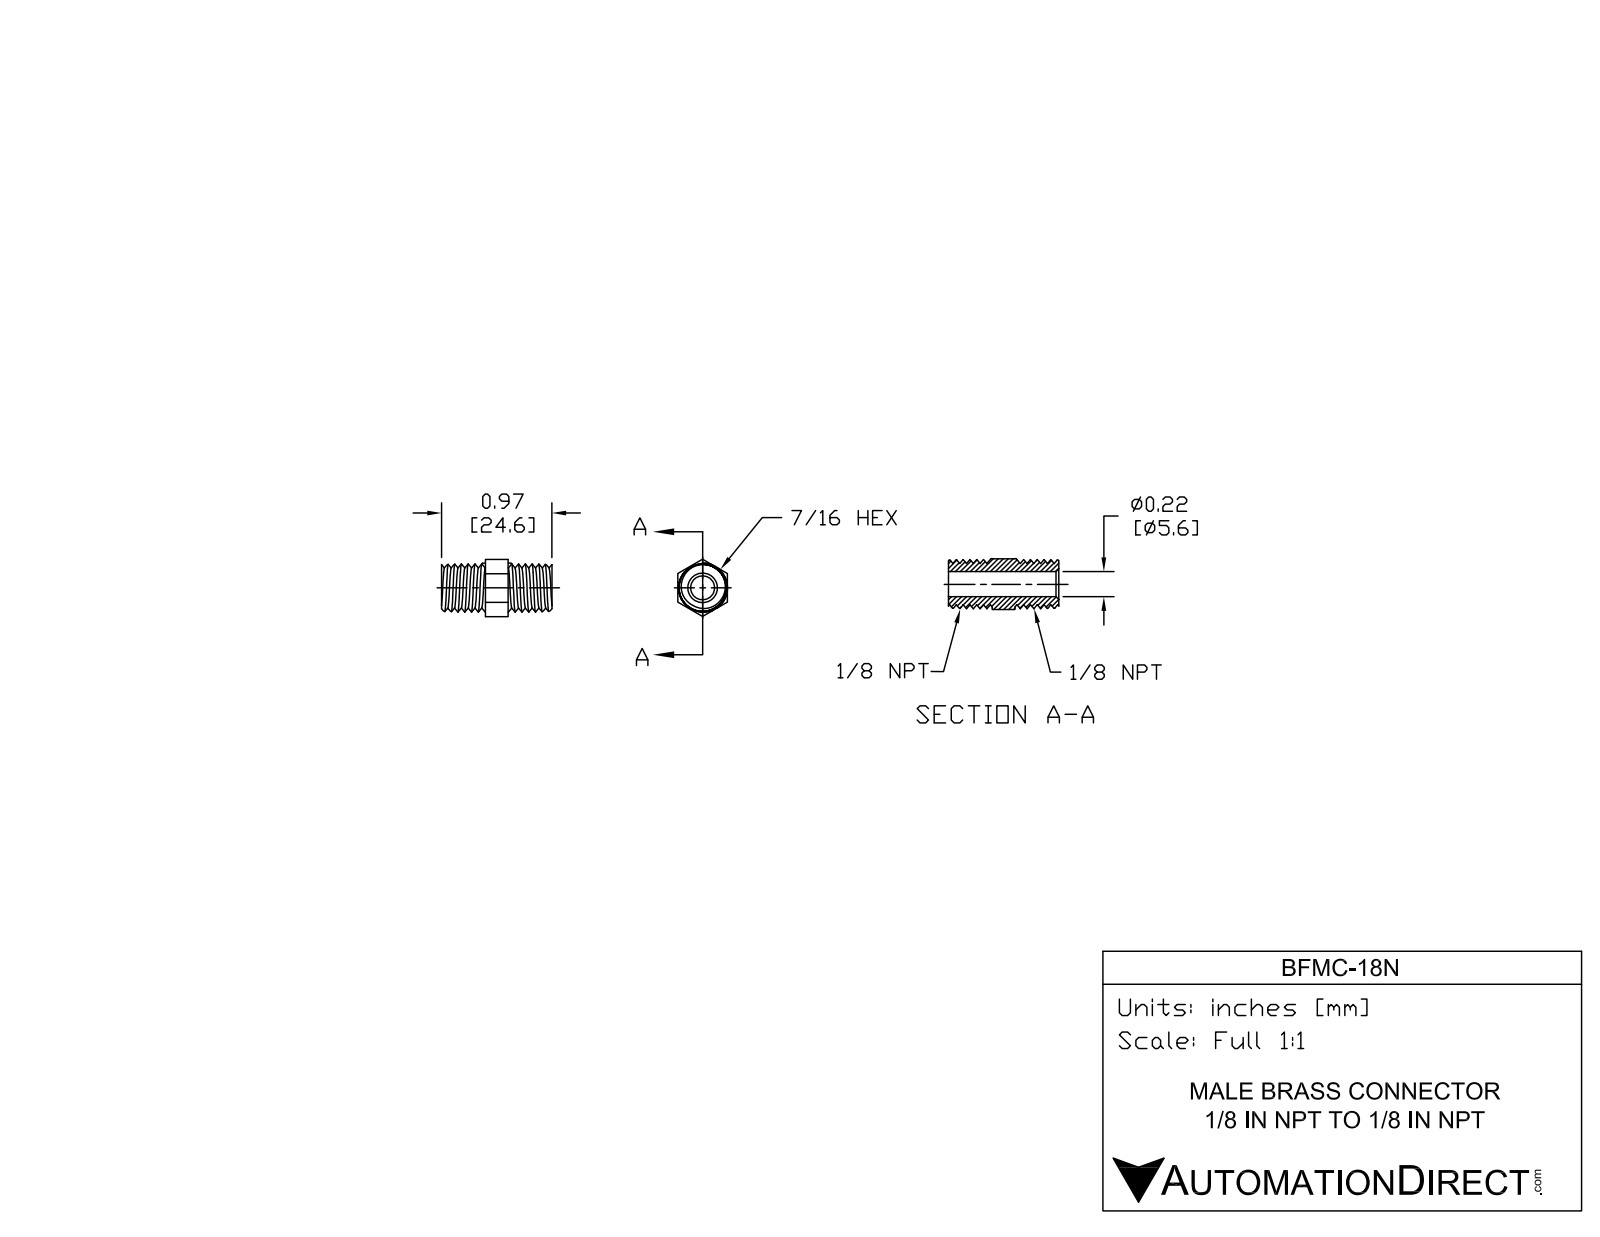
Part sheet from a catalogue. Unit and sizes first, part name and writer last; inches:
Units: inches
Overall size (bounding box): 0.975 × 0.505 × 0.438
Round holes (diameter × count): ⌀0.211 ×1
Main face-to-face distances: 0.438, 0.975, 0.387, 0.587, 0.2, 0.219
Volume: 0.09 in³ · Surface area: 2.622 in²
Bodies: 1 solid, 36 faces (12 planar, 2 cylindrical, 22 other)
Part name (STEP PRODUCT): BFMC-18N
STEP written by: SolidWorks 2015 (CONFIG_CONTROL_DESIGN)
